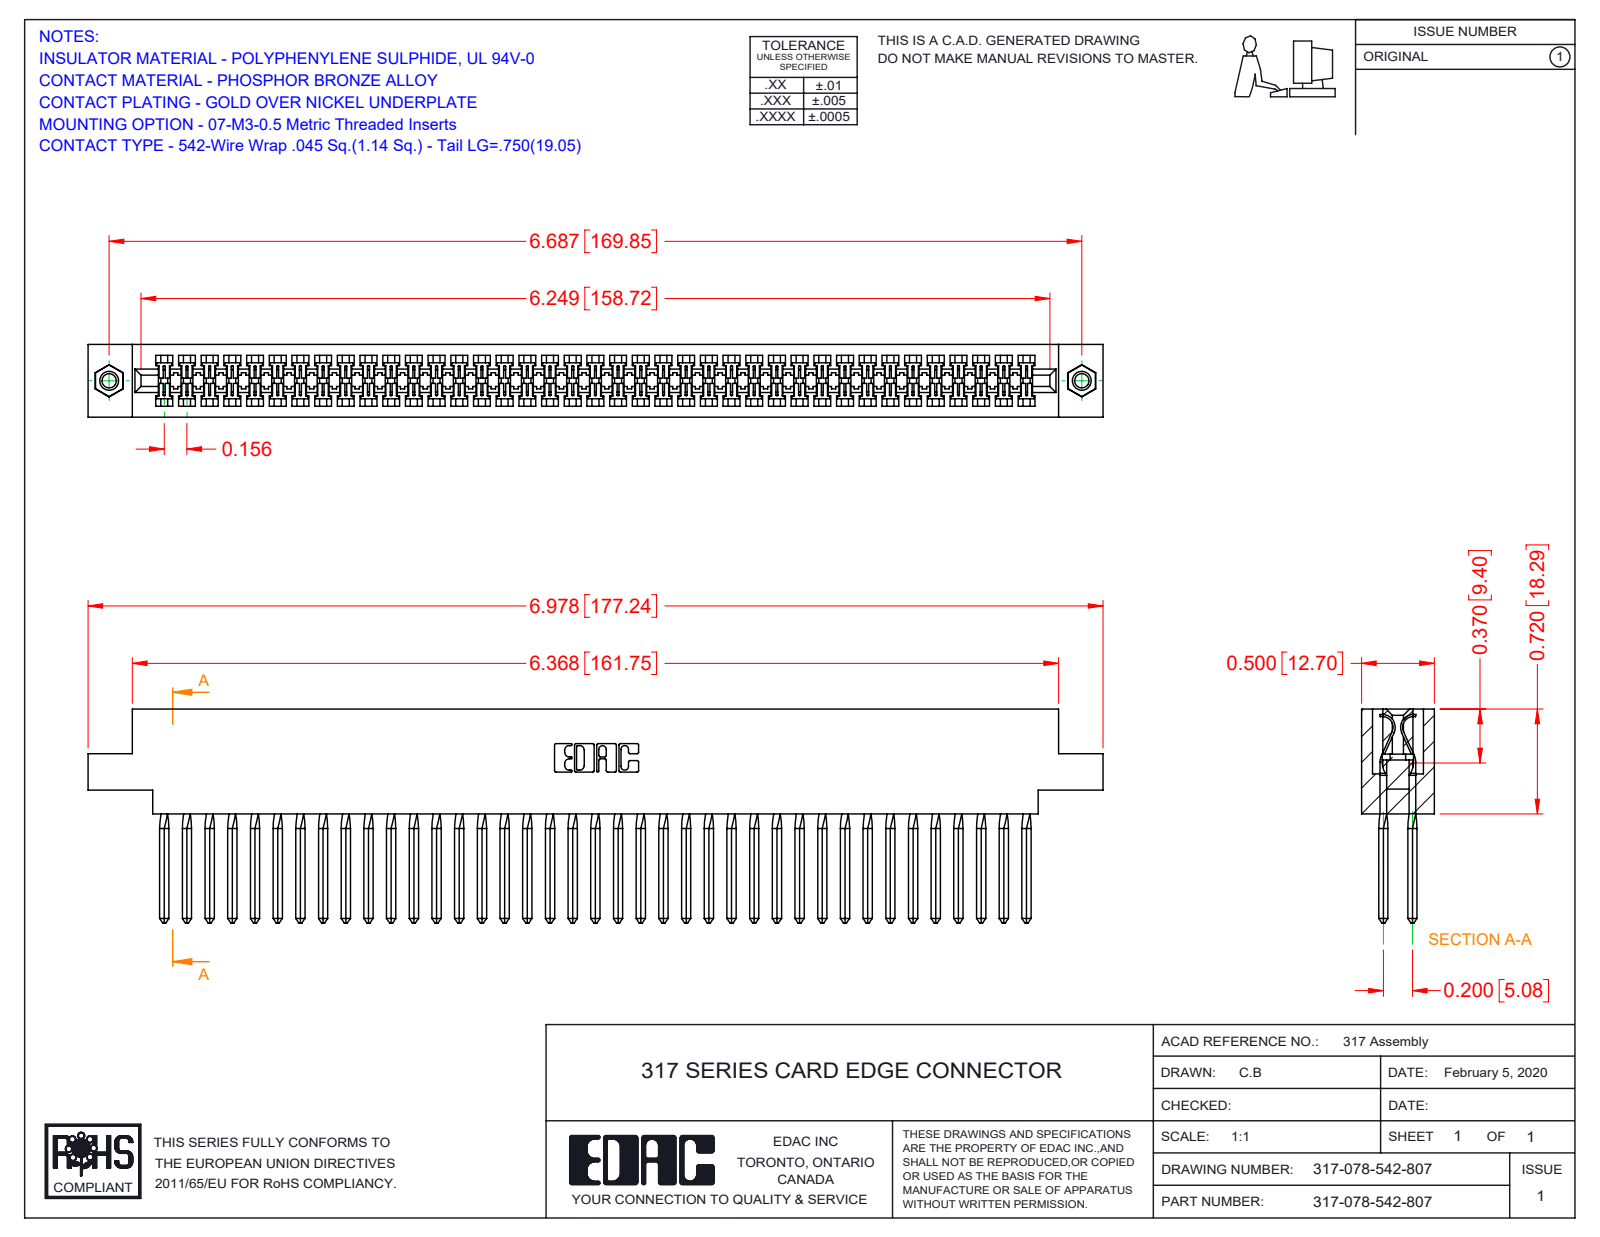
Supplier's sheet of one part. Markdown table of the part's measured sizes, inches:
| quantity | value |
| --- | --- |
| part name | 317-290-003_542; 317-078-542-807; 345-250-001_345-250-005-103; 317 Part_.156 Dia - TI |
| STEP written by | SolidWorks 2016 (CONFIG_CONTROL_DESIGN) |
| units | inches |
| bodies | 81 solids, 4608 faces (3678 planar, 602 cylindrical, 328 other) |
| overall size | 6.978 × 1.47 × 0.5 |
| volume | 1.764 in³ |
| surface area | 62.23 in² |
| round holes (diameter × count) | 0.098 × 2, 0.125 × 2, 0.156 × 2 |
| round bosses / shafts (diameter × count) | 0.155 × 2 |
| partial cylindrical surfaces (radius × count) | 0.006 × 156, 0.01 × 22, 0.007 × 6, 0.031 × 6, 0.026 × 3, 0.074 × 2, 0.089 × 2, 0.1 × 2 |
| main face-to-face distances | 0.5, 0.075, 0.425, 0.35, 0.2, 0.046, 0.128, 0.372, 0.052, 0.297 |
| hole center spacings | 6.687 |
